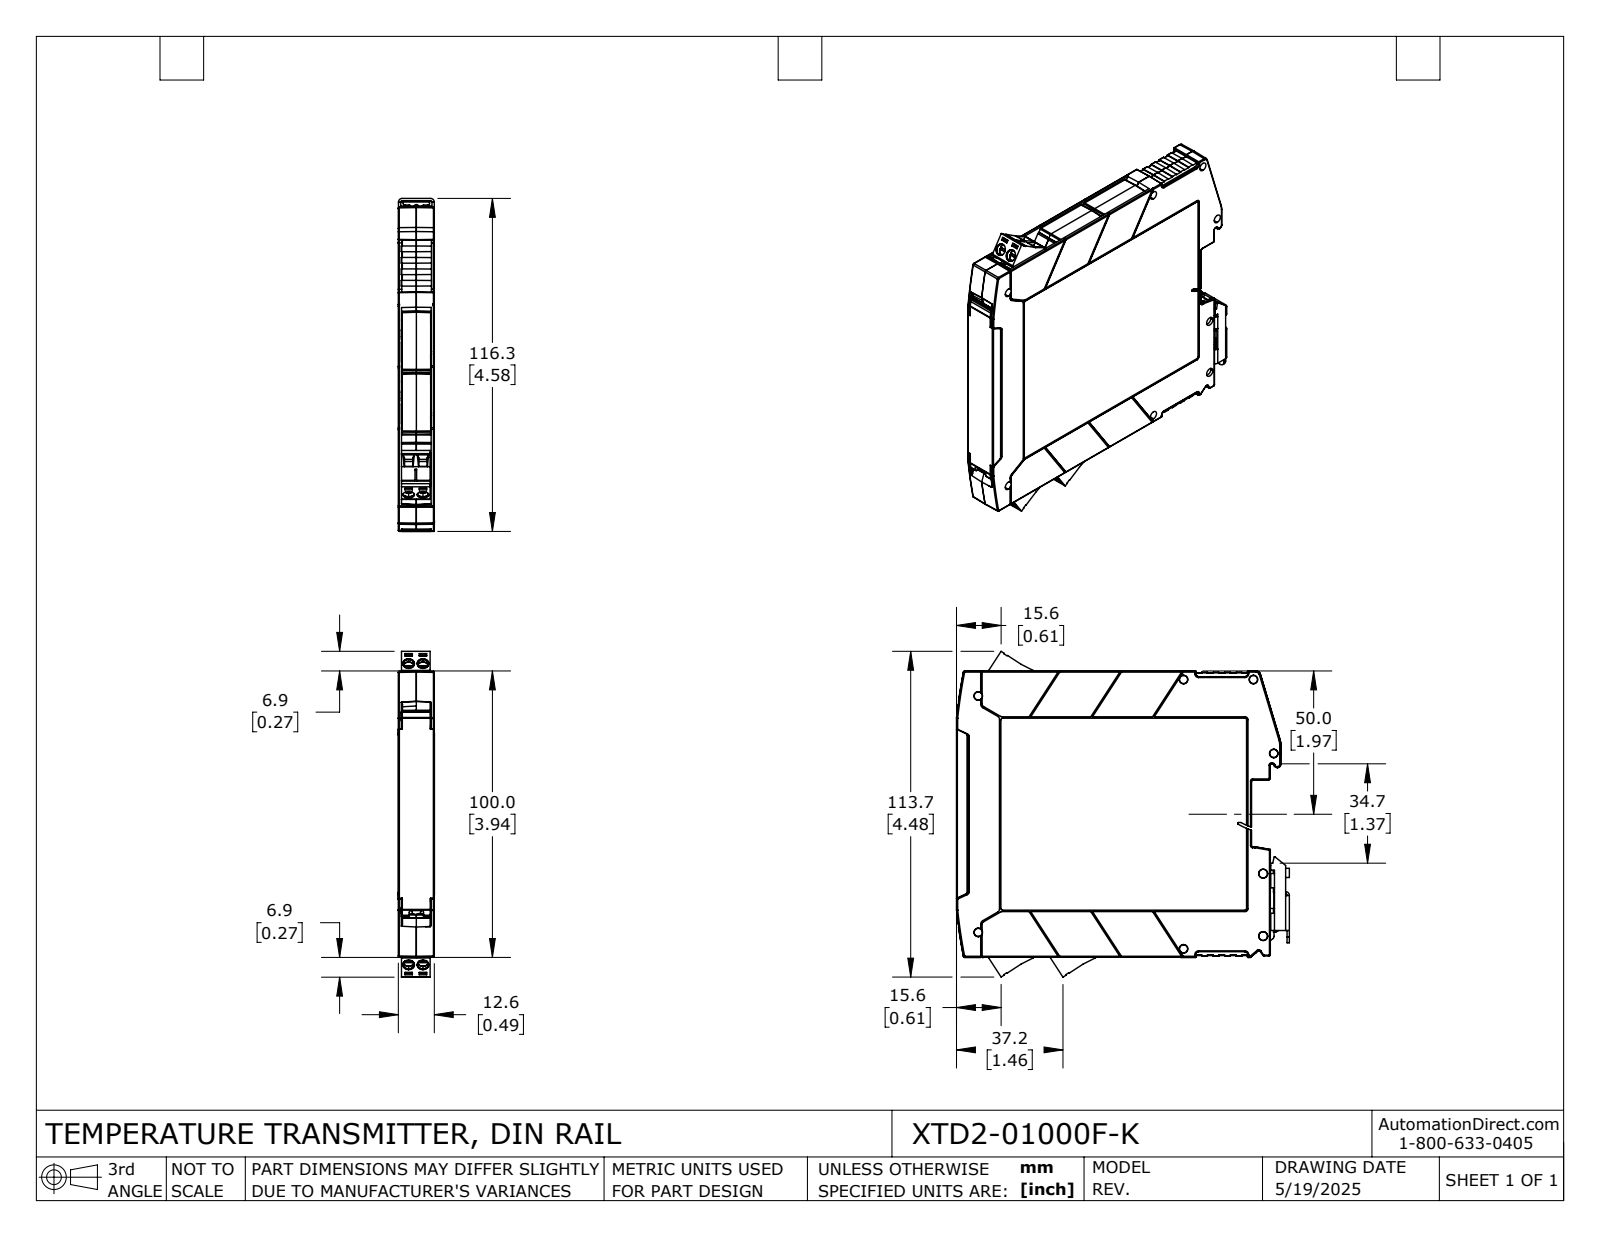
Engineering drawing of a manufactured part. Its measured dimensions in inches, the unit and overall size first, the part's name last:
Units: inches
Overall size (bounding box): 4.577 × 4.478 × 0.496
Round holes (diameter × count): ⌀0.063 ×6, ⌀0.11 ×6, ⌀0.152 ×6, ⌀0.159 ×6
Round bosses / shafts (diameter × count): ⌀0.156 ×6, ⌀0.098 ×6, ⌀0.059 ×2, ⌀0.053 ×2
Partial cylindrical surfaces — rounded edges, fillets, slot ends (radius × count): R0.008 ×89, R0.012 ×78, R0.02 ×71, R0.039 ×22, R0.004 ×20, R0.016 ×13, R0.006 ×12, R0.028 ×8
Main face-to-face distances: 0.049, 0.445, 0.494, 0.396, 0.043, 0.451, 0.402, 0.031, 0.198, 0.247
Hole centre spacings: 0.197, 0.464, 0.504, 0.713, 0.739
Volume: 2.41 in³ · Surface area: 101.5 in²
Bodies: 14 solids, 3337 faces (1910 planar, 596 cylindrical, 831 other)
Part name (STEP PRODUCT): XTD2-01000F-K
STEP written by: SolidWorks 2024 (AUTOMOTIVE_DESIGN)
